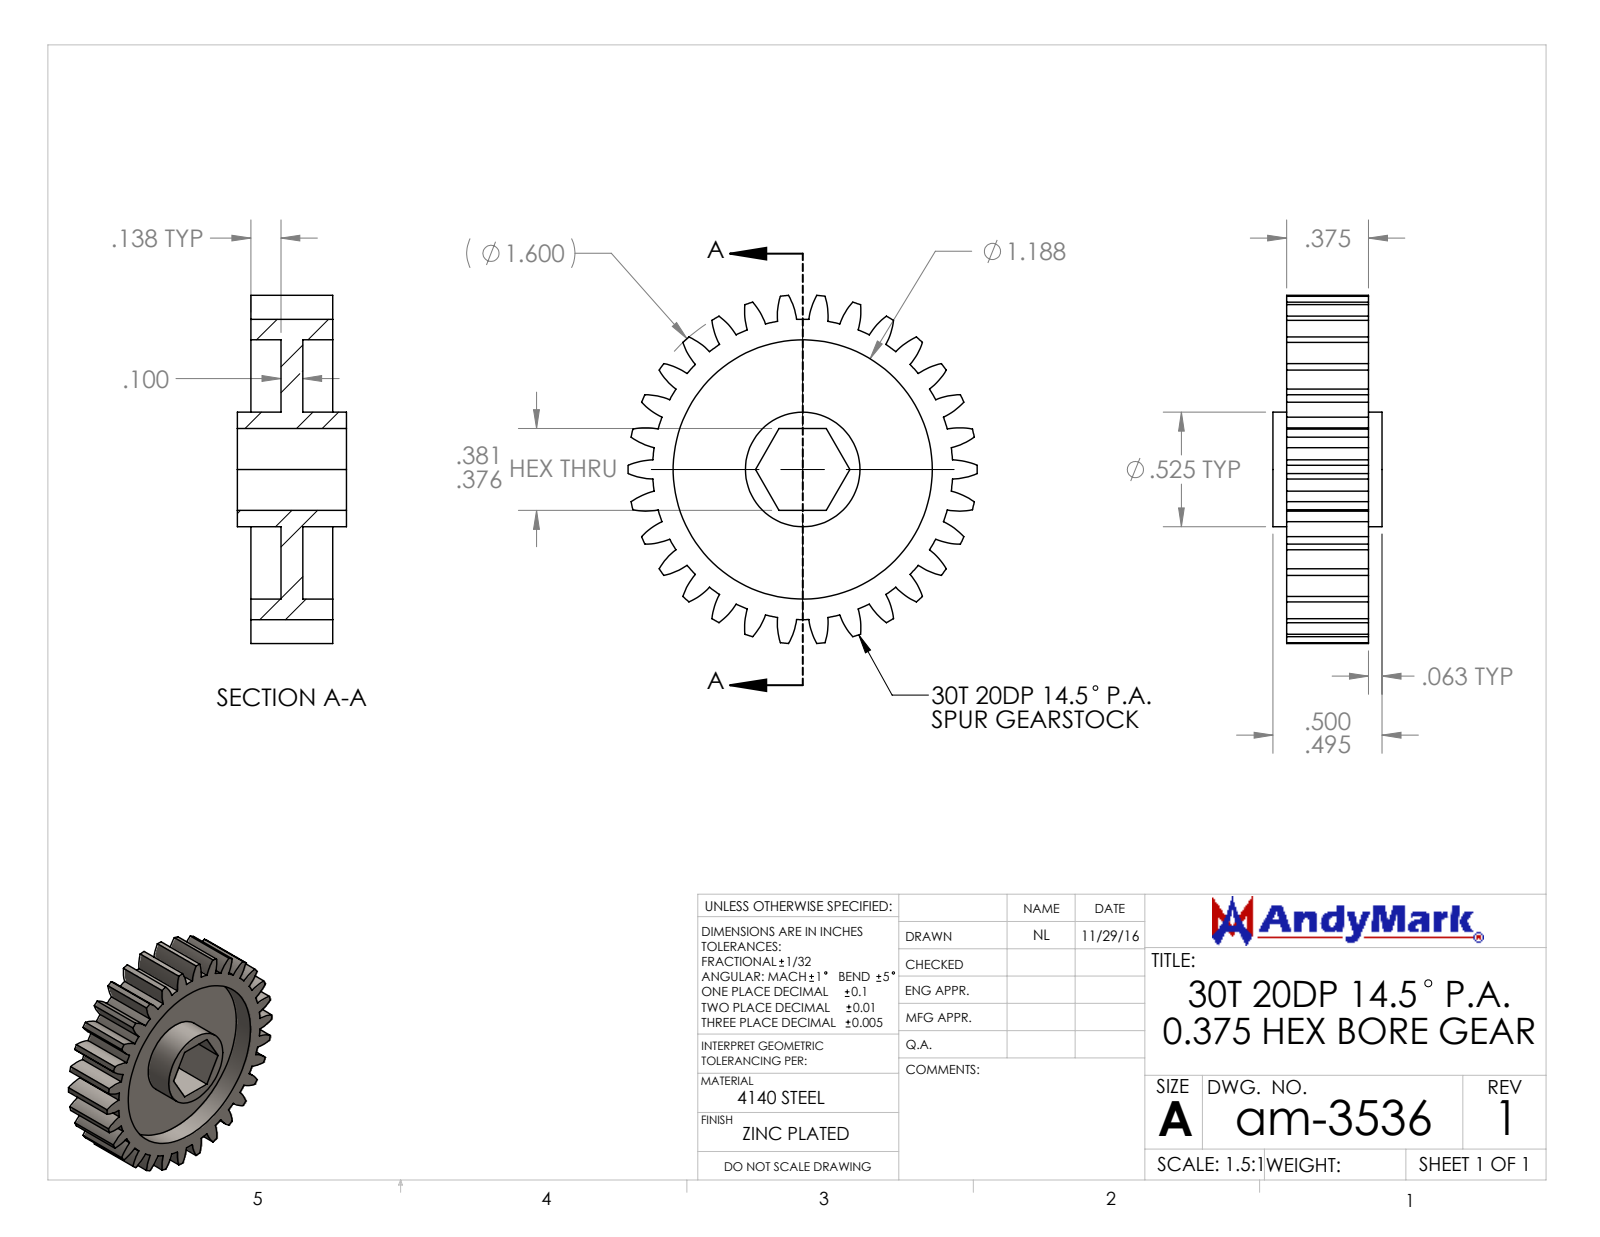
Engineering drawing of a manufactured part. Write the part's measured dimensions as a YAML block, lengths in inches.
part_name: "am-3536 30T 20DP 375hex 375 FW"
step_written_by: "SolidWorks 2014 (AUTOMOTIVE_DESIGN)"
units: inches
bodies: {solids: 1, faces: 145, planar: 12, cylindrical: 133, other: 0}
overall_size: [1.6, 1.595, 0.5]
volume: 0.368
surface_area: 9.22
round_holes:
  - {diameter: 1.187, count: 1}
round_bosses_or_shafts:
  - {diameter: 0.525, count: 1}
partial_cylinders:
  - {radius: 0.3, count: 60}
  - {radius: 0.688, count: 1}
  - {radius: 0.8, count: 1}
face_to_face_distances: [0.1, 0.137, 0.237, 0.375, 0.238, 0.138, 0.375, 0.2, 0.3, 0.063]
